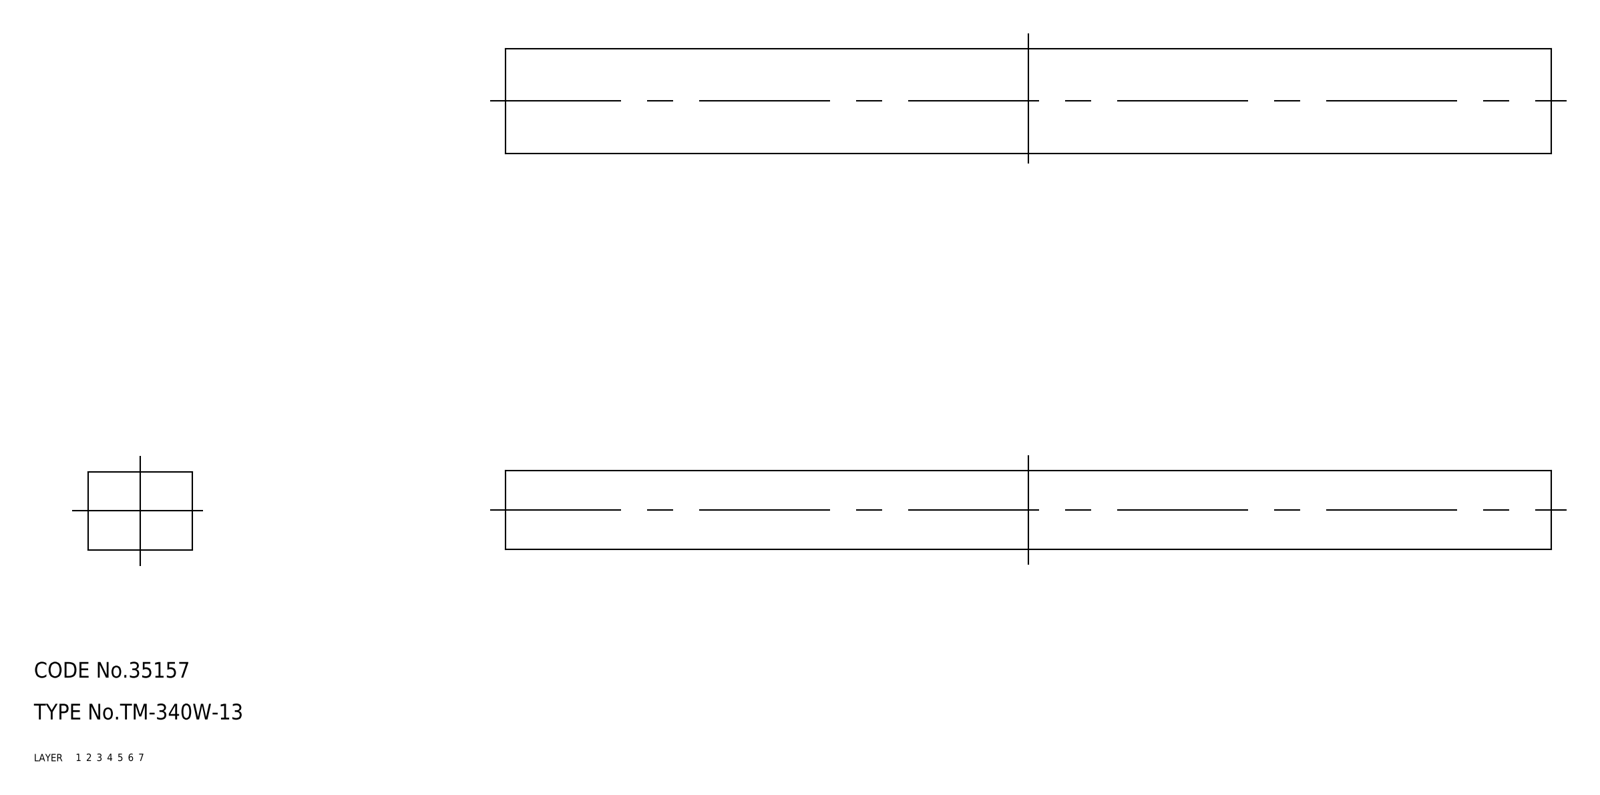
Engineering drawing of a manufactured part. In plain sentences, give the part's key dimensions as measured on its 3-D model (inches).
The part is named "rubber foam; TM_340W_13". Its 3-D file was written by "SolidWorks 2015 (AUTOMOTIVE_DESIGN)". It is 1 solid with 6 faces: 6 planar, 0 cylindrical and 0 other. Overall it measures 7.874 by 0.787 by 0.591 inches. Its volume is 3.661 cubic inches and its surface area 22.63 square inches. The main face-to-face distances are 0.591, 0.787, 7.874.
